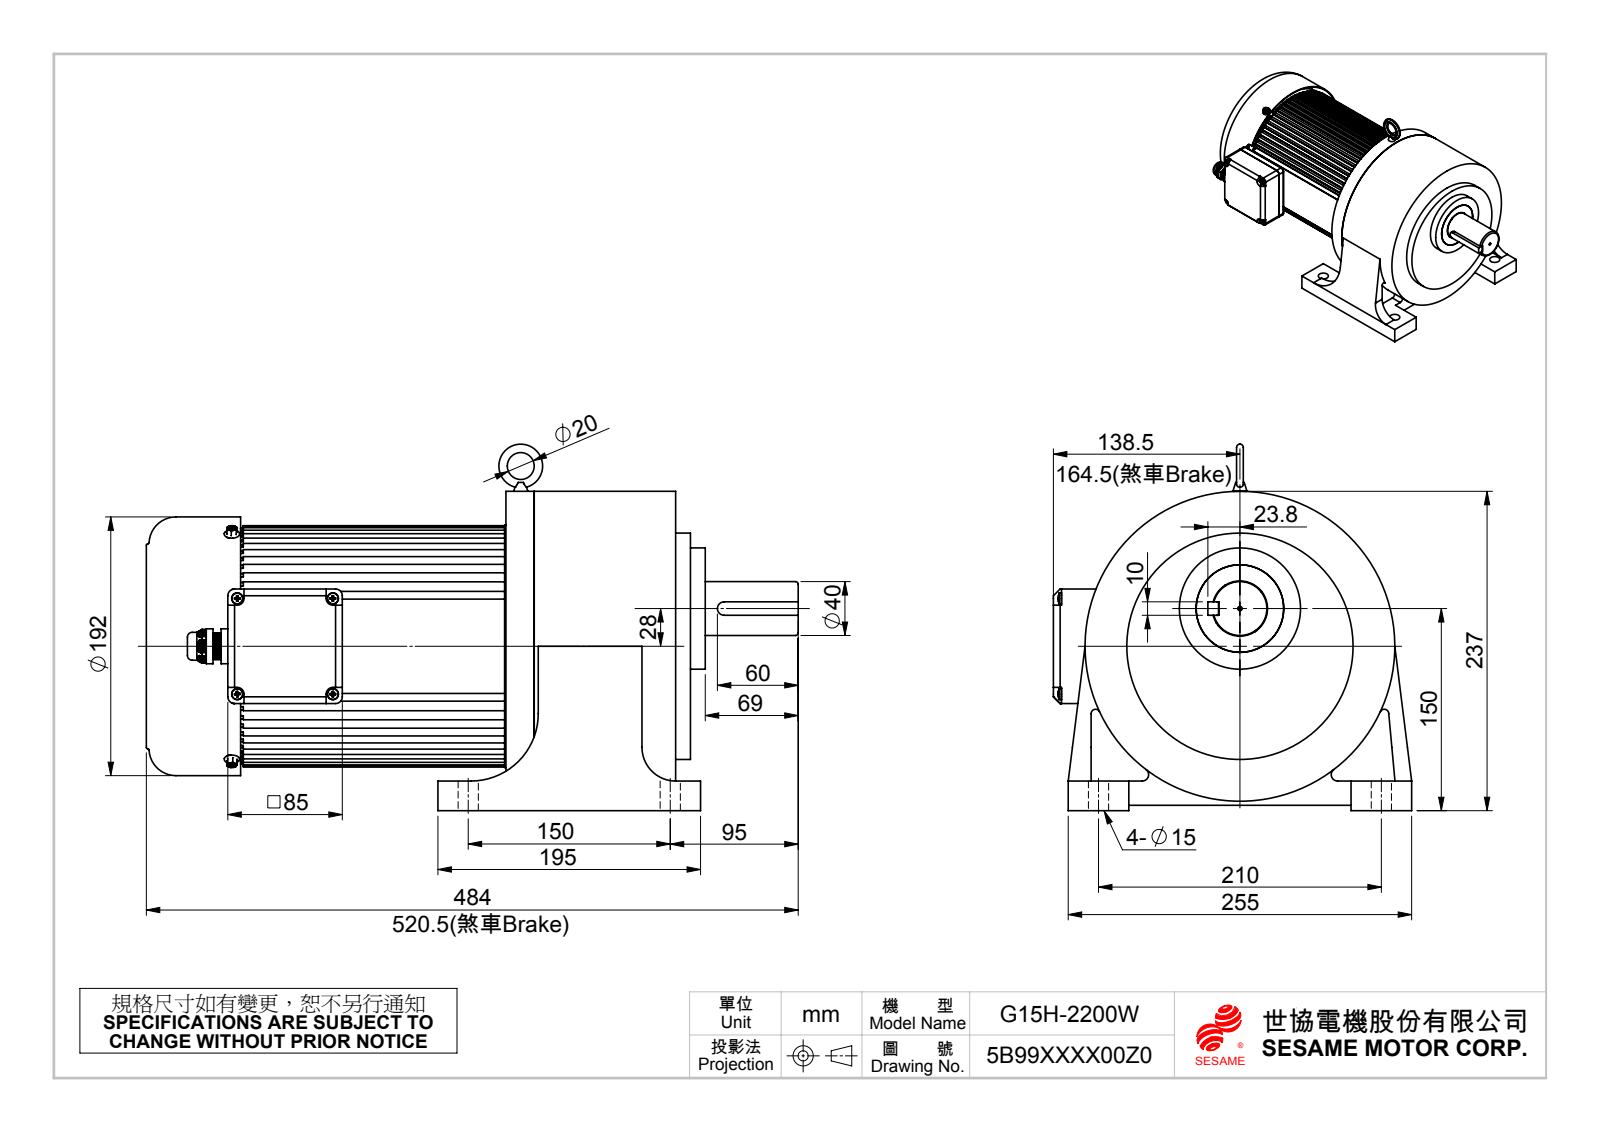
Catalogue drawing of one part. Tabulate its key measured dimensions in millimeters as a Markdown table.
| quantity | value |
| --- | --- |
| part name | (標準品)G15H2200W(5B99XXX100)(減速比共用); 出線盒墊片JTH-UP3(PVC2mm厚); 油封40x65x10; 成品-塑膠T盒 (+8 more) |
| STEP written by | SolidWorks 2010 (CONFIG_CONTROL_DESIGN) |
| units | millimeters |
| bodies | 20 solids, 3340 faces (1242 planar, 1070 cylindrical, 1028 other) |
| overall size | 484 × 272 × 266 |
| volume | 12 220 000 mm³ |
| surface area | 872 353 mm² |
| round holes (diameter × count) | 5 × 11, 3.3 × 9, 6 × 4, 8 × 4, 15 × 4, 4.2 × 3, 2 × 1, 6.5 × 1, 6.8 × 1, 10.8 × 1, 16.5 × 1, 20 × 1 |
| round bosses / shafts (diameter × count) | 8.3 × 4, 4 × 4, 5 × 3, 230 × 1, 218 × 1, 192 × 1, 190 × 1, 180 × 1 |
| partial cylindrical surfaces (radius × count) | 0.1 × 118, 1.5 × 59, 1 × 24, 0.5 × 18, 5 × 10, 2.9 × 6, 2 × 4, 2.55 × 4 |
| main face-to-face distances | 5, 22, 27, 4, 3, 266, 1, 10, 198, 220 |
| hole center spacings | 45, 58.25, 71, 82.38, 11, 11.5, 14.6, 14.79 |
